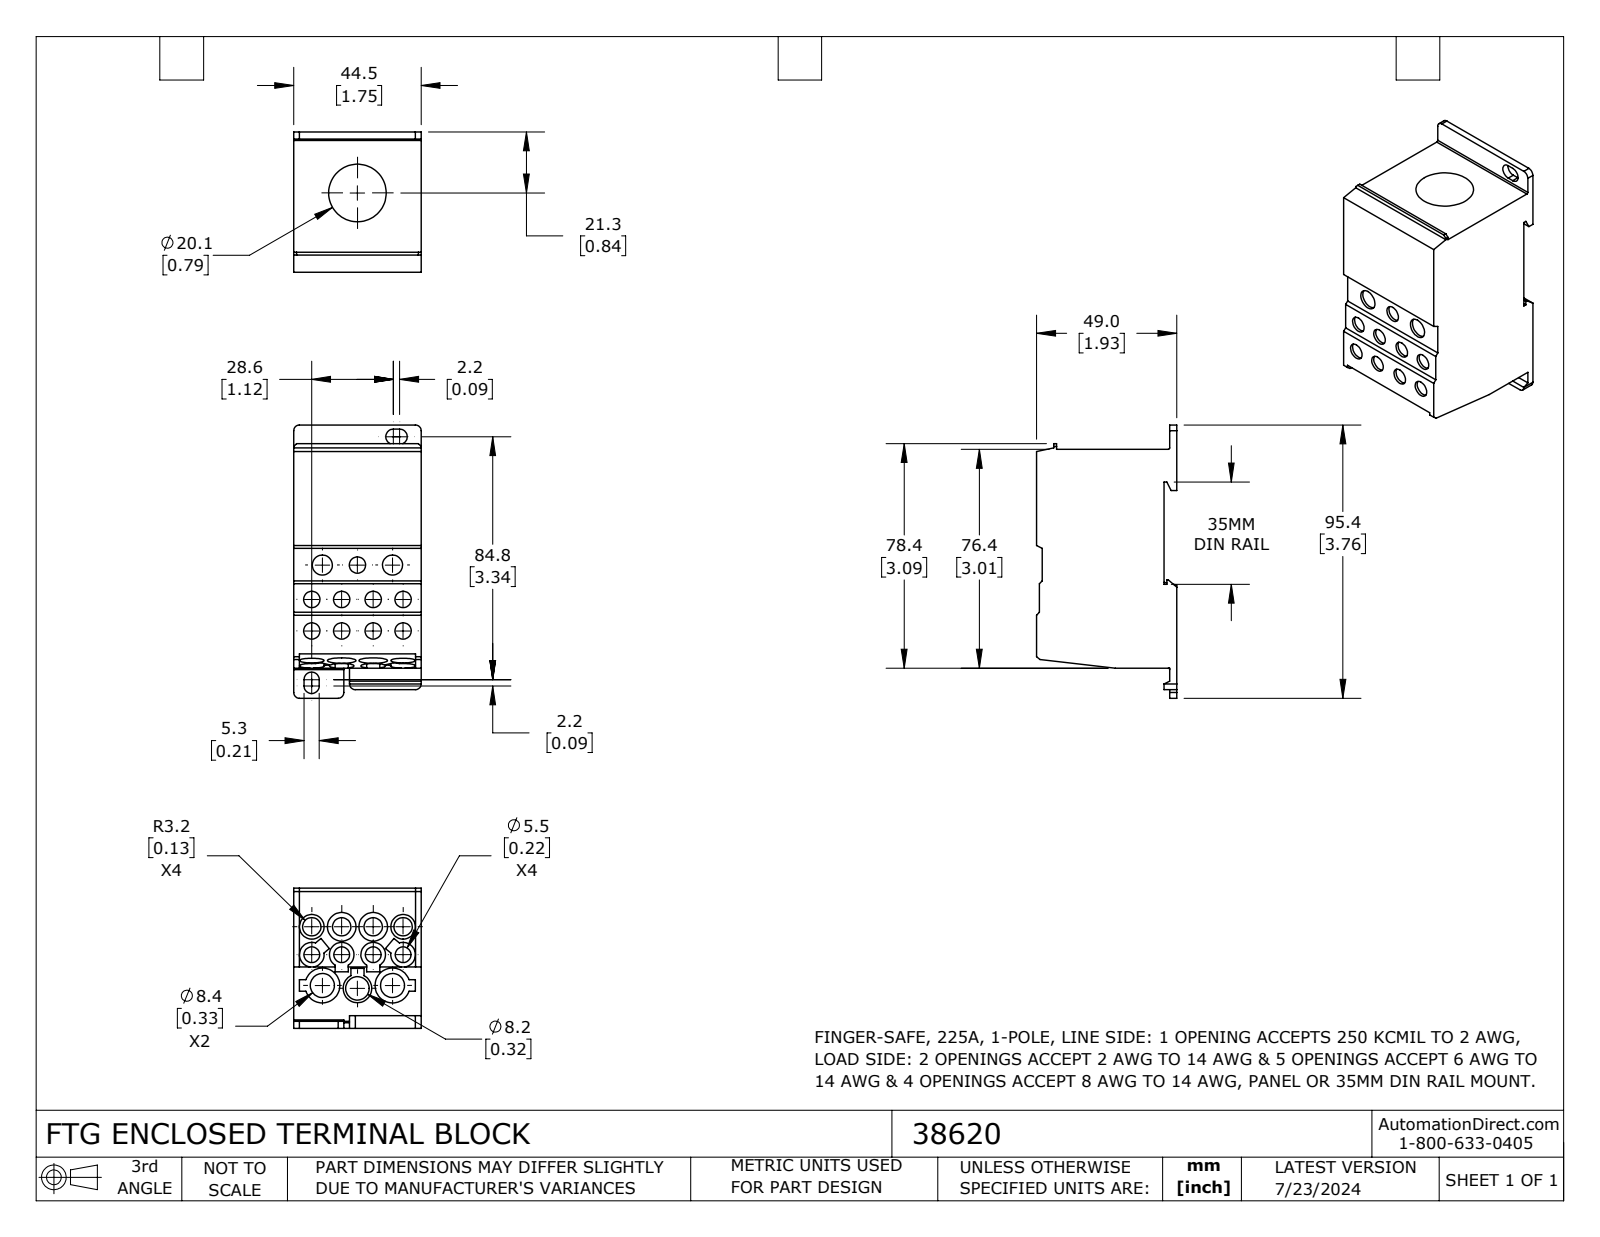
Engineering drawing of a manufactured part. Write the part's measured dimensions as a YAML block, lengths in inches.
part_name: "38620"
step_written_by: "SolidWorks 2023 (CONFIG_CONTROL_DESIGN)"
units: inches
bodies: {solids: 1, faces: 233, planar: 100, cylindrical: 91, other: 42}
overall_size: [3.756, 1.929, 1.752]
volume: 7.679
surface_area: 49.18
round_holes:
  - {diameter: 0.224, count: 9}
  - {diameter: 0.339, count: 6}
  - {diameter: 0.244, count: 4}
  - {diameter: 0.268, count: 4}
  - {diameter: 0.331, count: 3}
  - {diameter: 0.394, count: 3}
  - {diameter: 0.276, count: 2}
  - {diameter: 0.354, count: 2}
  - {diameter: 0.48, count: 2}
  - {diameter: 0.791, count: 1}
partial_cylinders:
  - {radius: 0.079, count: 6}
  - {radius: 0.104, count: 4}
  - {radius: 0.02, count: 2}
face_to_face_distances: [1.752, 1.929, 0.177, 0.079, 0.039, 1.673, 1.791, 0.098, 1.831, 1.713]
hole_center_spacings: [0.411, 0.844, 0.433, 1.256, 0.384, 0.563, 0.928, 0.931]
